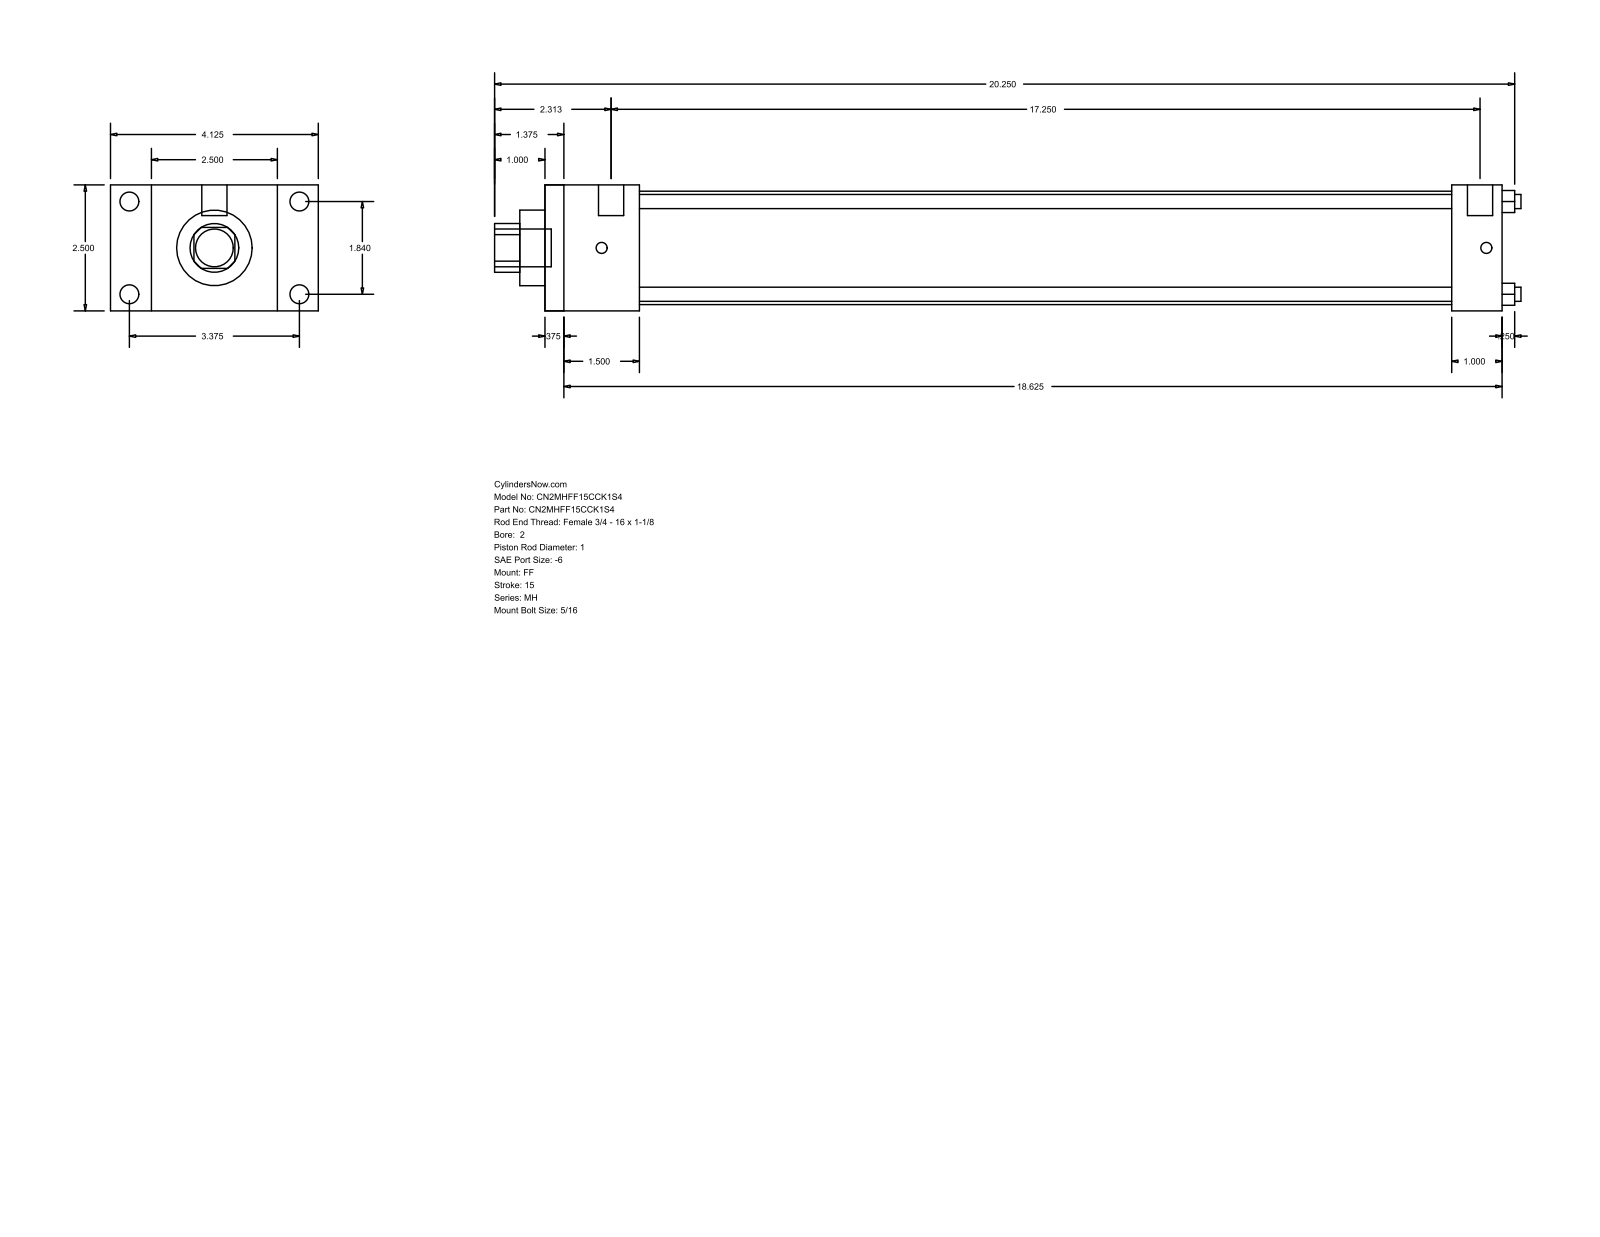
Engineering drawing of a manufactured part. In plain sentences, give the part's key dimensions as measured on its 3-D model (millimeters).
The part is named "MH_FF__0200_1". Its 3-D file was written by "GSSL Pune (CONFIG_CONTROL_DESIGN)". It is 0 solids with 92 faces: 64 planar, 28 cylindrical and 0 other. Overall it measures 517.52 by 104.78 by 63.5 millimeters. Round holes: 4 of diameter 7.14, 1 of diameter 25.4, 1 of diameter 38.1, 1 of diameter 57.15. Round bosses or shafts: 4 of diameter 9.53, 4 of diameter 5.56, 2 of diameter 12.7, 1 of diameter 19.05. Partial cylindrical surfaces (rounded edges, fillets, slot ends): 1 of radius 12.29. The main face-to-face distances are 63.5, 482.6, 9.52, 473.08, 20.64, 25.4, 47.63, 457.2, 38.11, 447.68. The hole center spacings are 33.05, 46.74, 66.1.
